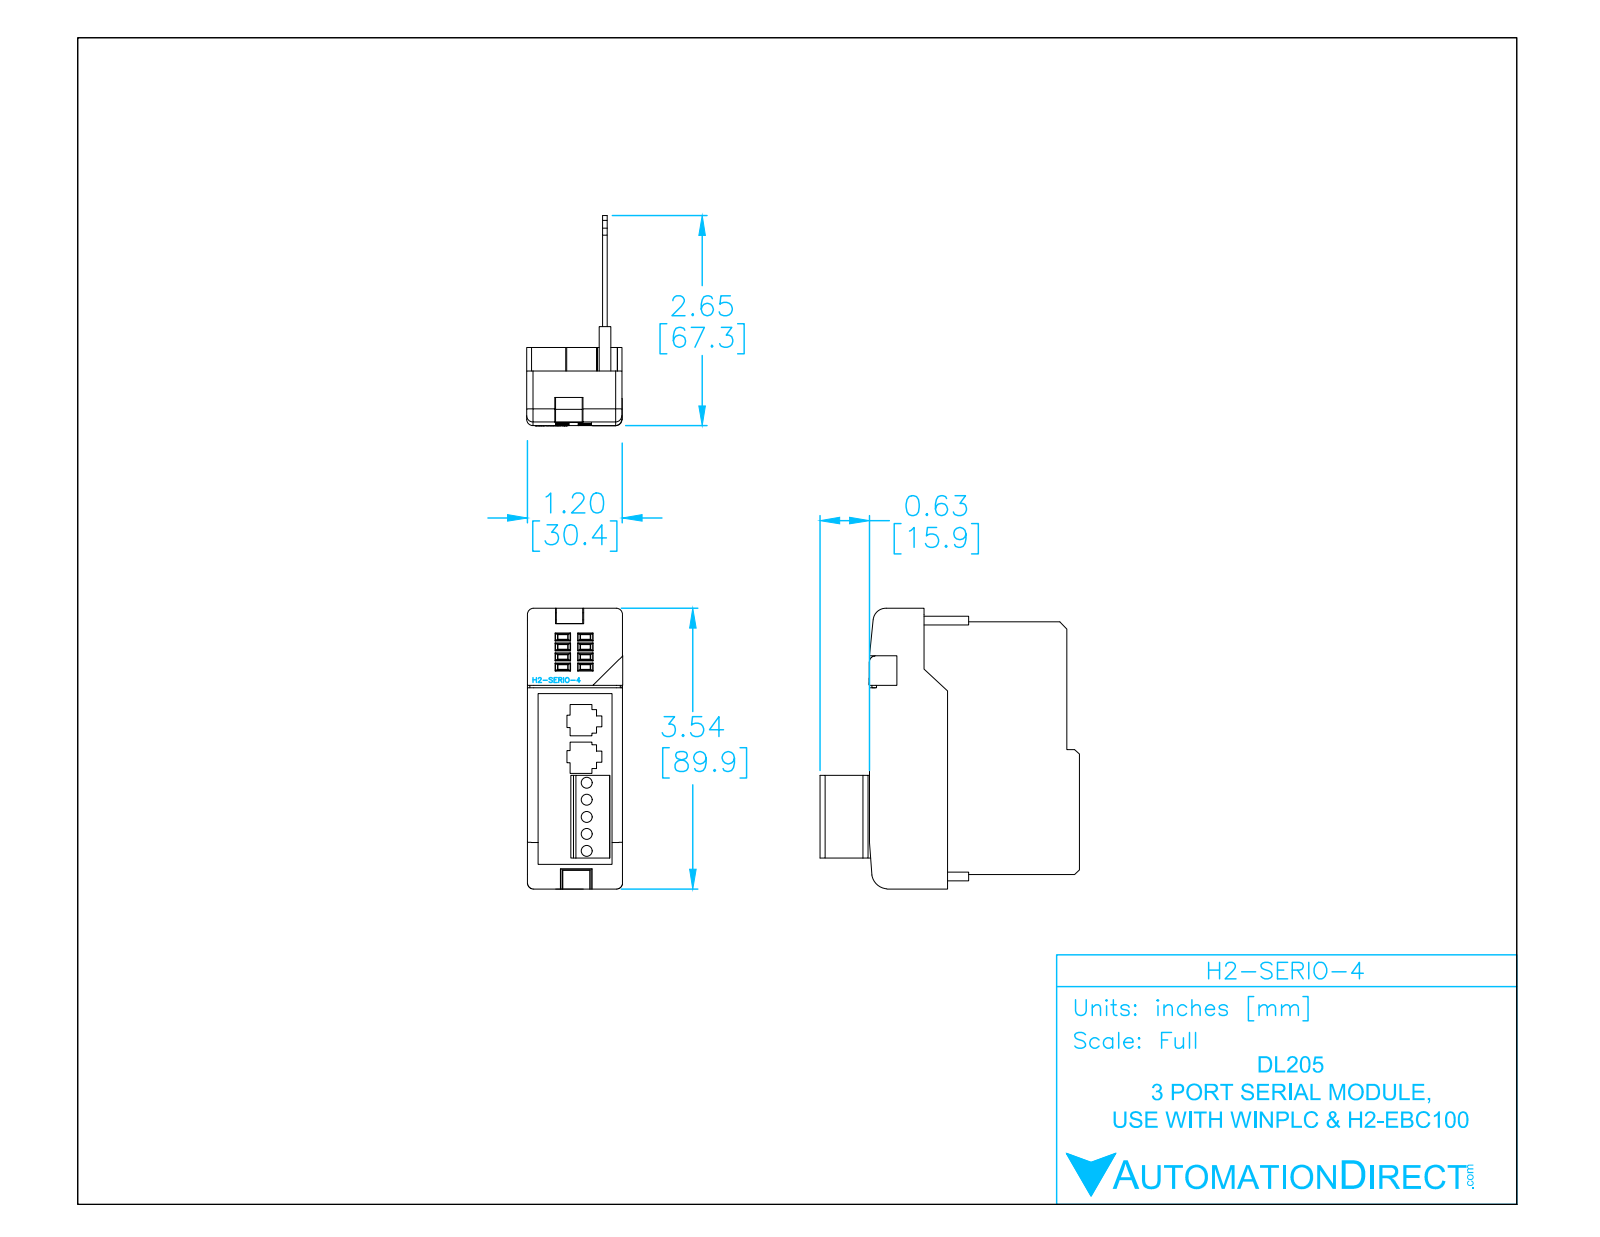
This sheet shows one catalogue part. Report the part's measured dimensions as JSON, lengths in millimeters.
{"part_name": "H2-SERIO-4", "step_written_by": "SolidWorks 2009 (AUTOMOTIVE_DESIGN)", "units": "millimeters", "bodies": {"solids": 1, "faces": 536, "planar": 382, "cylindrical": 104, "other": 50}, "overall_size": [90, 83.18, 30.55], "volume_mm3": 23900, "surface_area_mm2": 31951, "round_holes": [[3.56, 5]], "partial_cylinders_radius": [[0.5, 28], [2, 11], [3.01, 5], [0.25, 4], [1, 2], [2.62, 1], [3.79, 1], [4.12, 1]], "face_to_face_distances": [1.5, 4.72, 3.22, 6.22, 0.5, 24.28, 29, 2, 8.5, 25.78], "hole_center_spacings": [5.46, 10.92, 16.38, 21.84]}
